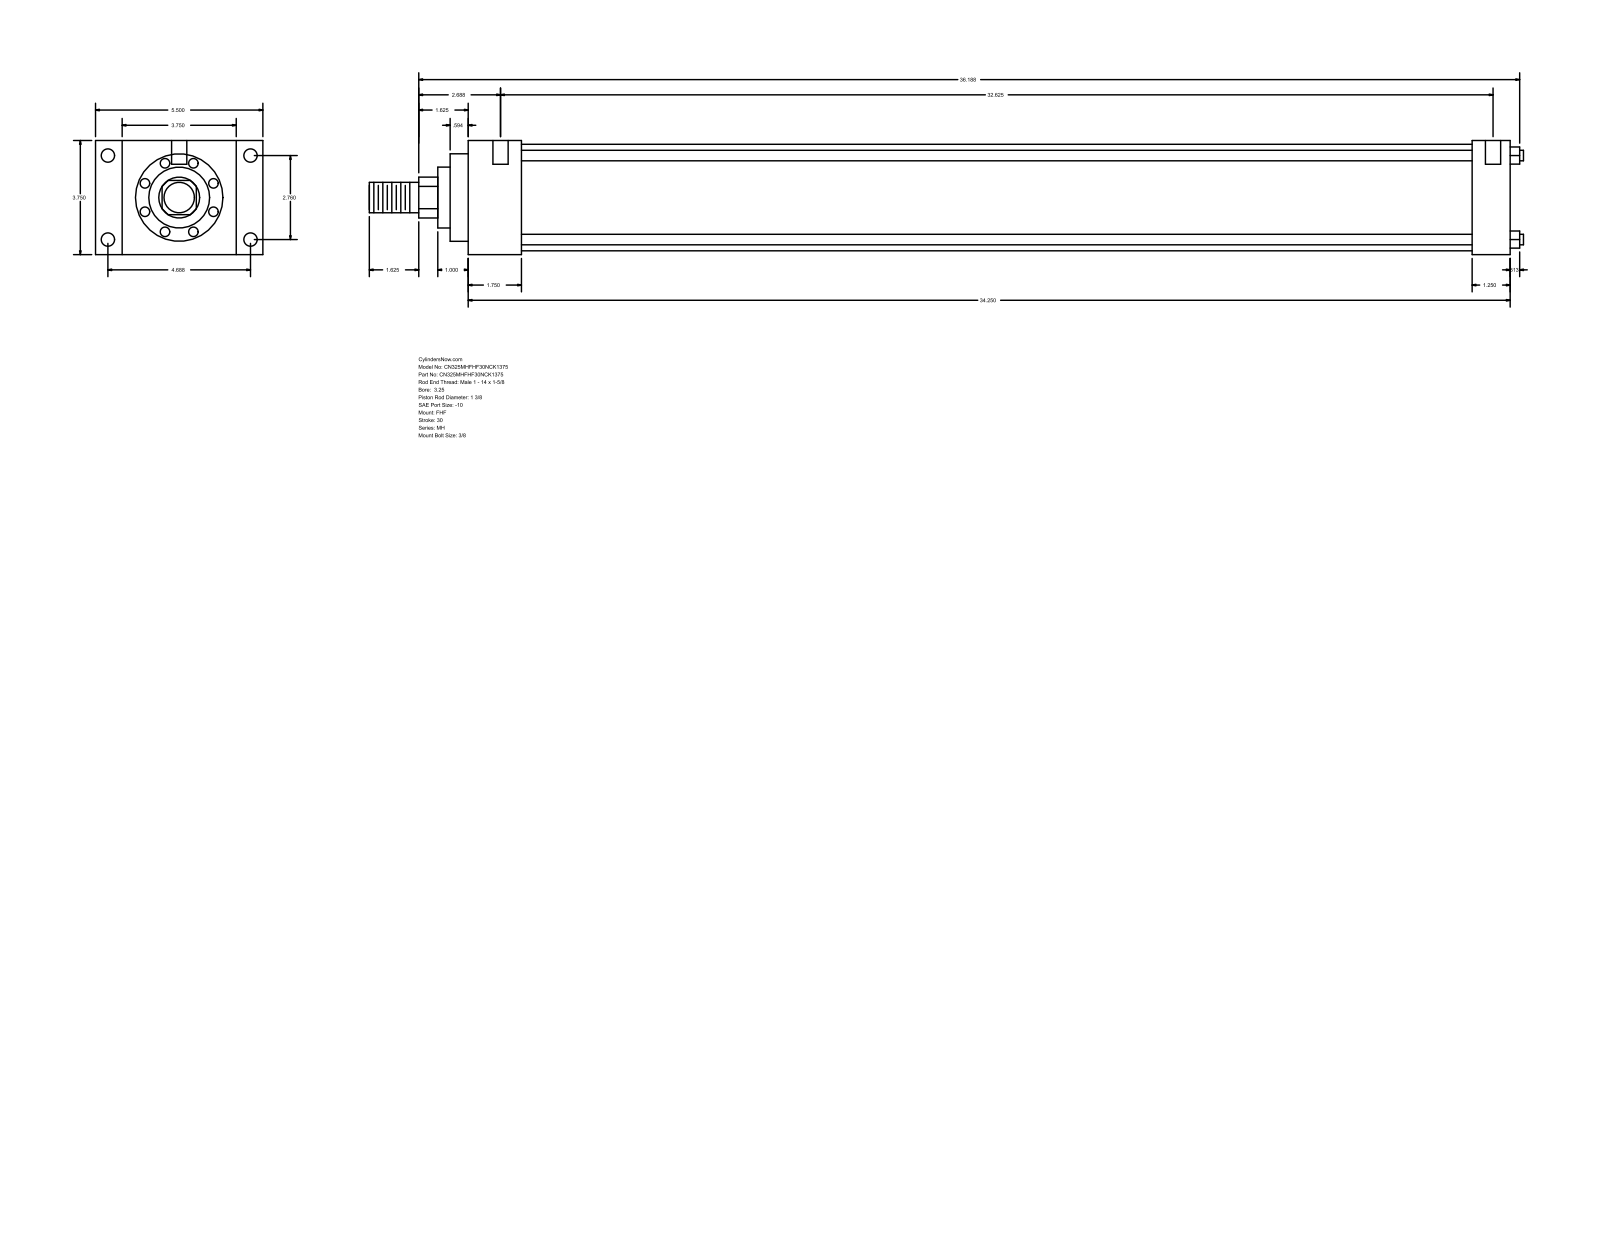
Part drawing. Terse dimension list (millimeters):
name: MH_FHF__0325_1.375
written by: GSSL Pune (CONFIG_CONTROL_DESIGN)
unit: mm
bodies: 0 solids, 90 faces (61 planar, 29 cylindrical, 0 other)
size: 963.61 × 139.7 × 95.25
holes: 4× ⌀5.56, 4× ⌀11.13, 2× ⌀12.7
bosses: 4× ⌀8.76, 1× ⌀88.9, 1× ⌀73.03, 1× ⌀50.8, 1× ⌀34.92, 1× ⌀25.4
rounds: 1× R17.06
face distances: 95.24, 869.96, 44.45, 825.51, 22.23, 117.47, 139.7, 838.21, 793.76, 31.75
hole spacings: 70.1, 119.06, 138.16, 835.03, 1.59, 4.76, 828.68, 830.27
